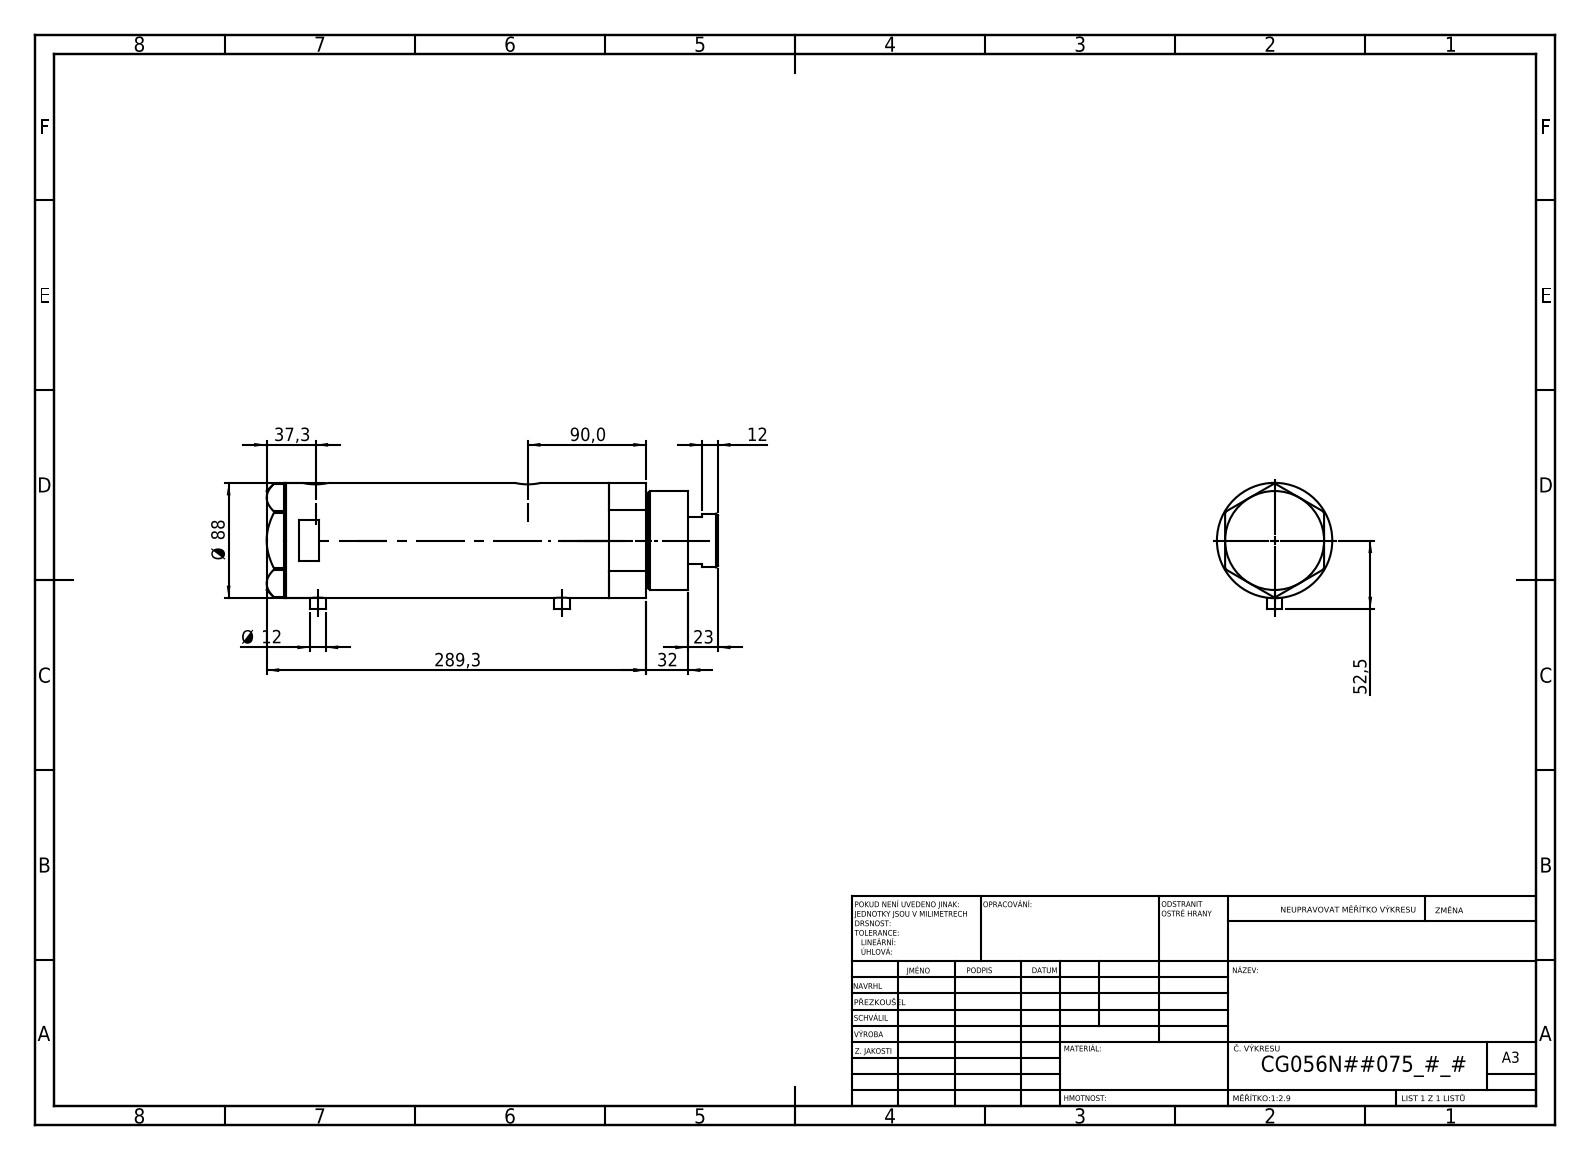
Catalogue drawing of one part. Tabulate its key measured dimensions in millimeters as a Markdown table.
| quantity | value |
| --- | --- |
| part name | V270CG_VC; V270CG_FRONT; V270CG_MIDDLE; V270CG_BACK |
| STEP written by | SolidWorks 2019 (CONFIG_CONTROL_DESIGN) |
| units | millimeters |
| bodies | 4 solids, 121 faces (52 planar, 49 cylindrical, 20 other) |
| overall size | 344.3 × 96.5 × 88 |
| volume | 1 811 000 mm³ |
| surface area | 251 750 mm² |
| round holes (diameter × count) | 12.5 × 2, 13.16 × 2, 20 × 2, 14.5 × 1, 42 × 1, 43.5 × 1, 56 × 1, 60 × 1, 80 × 1 |
| round bosses / shafts (diameter × count) | 12 × 2, 88 × 1, 75 × 1, 73 × 1, 41 × 1 |
| main face-to-face distances | 184.4, 26, 158.4, 15, 41, 199.4, 306.3, 321.3, 280.3, 121.9 |
| hole center spacings | 1.7, 25.8, 160.3, 162, 186.1, 187.8 |
